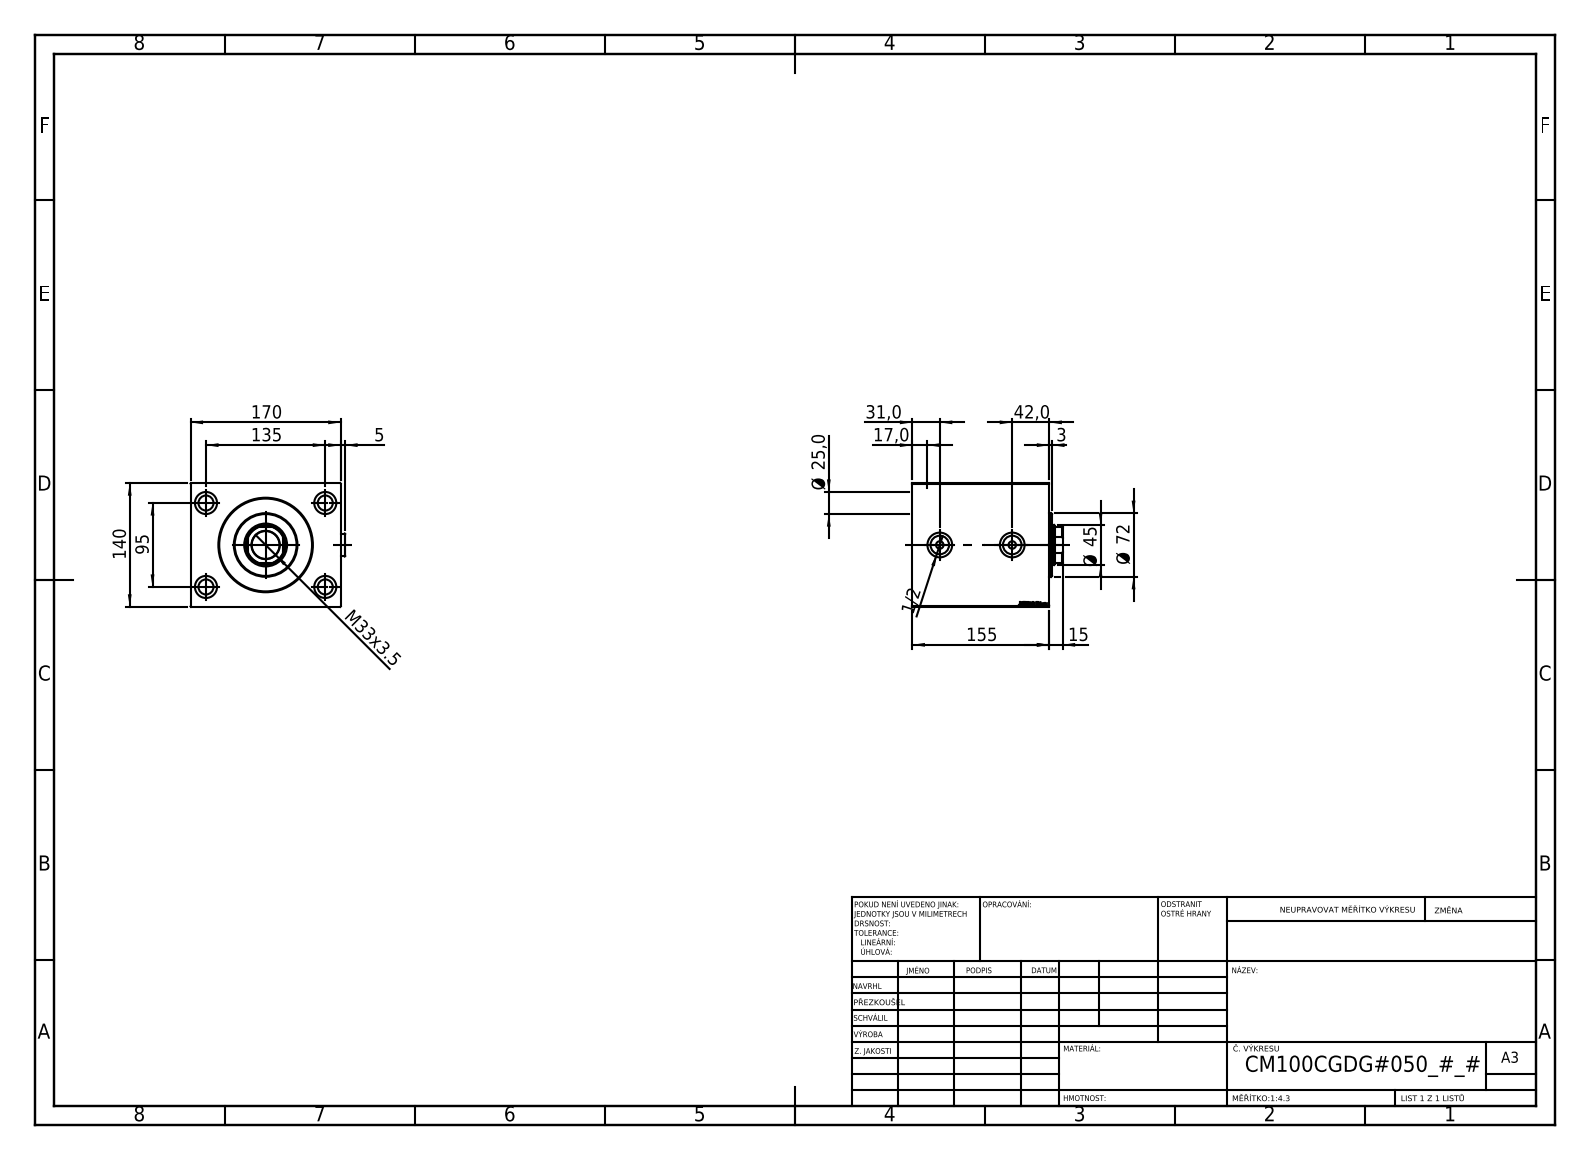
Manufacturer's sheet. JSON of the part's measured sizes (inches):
{"part_name": "V450CM_VC_B; V450CM_C_VCP; Zatka_OIL_PORT; V450CM_C_Body", "step_written_by": "SolidWorks 2019 (CONFIG_CONTROL_DESIGN)", "units": "inches", "bodies": {"solids": 5, "faces": 919, "planar": 443, "cylindrical": 78, "other": 398}, "overall_size": [6.886, 6.693, 5.512], "volume_in3": 193.9, "surface_area_in2": 465.4, "round_holes": [[0.669, 4], [0.984, 4], [0.335, 2], [0.825, 2], [1.102, 2], [1.24, 1], [1.772, 1], [1.909, 1], [3.937, 1], [4.016, 1], [4.134, 1]], "round_bosses_or_shafts": [[1.024, 2], [2.835, 1]], "partial_cylinders_radius": [[0.866, 1]], "face_to_face_distances": [5.512, 6.693, 6.102, 5.079, 1.024, 0.591, 4.488, 2.559, 1.969, 3.543], "hole_center_spacings": [3.25, 3.74, 5.315, 6.499, 3.228]}
